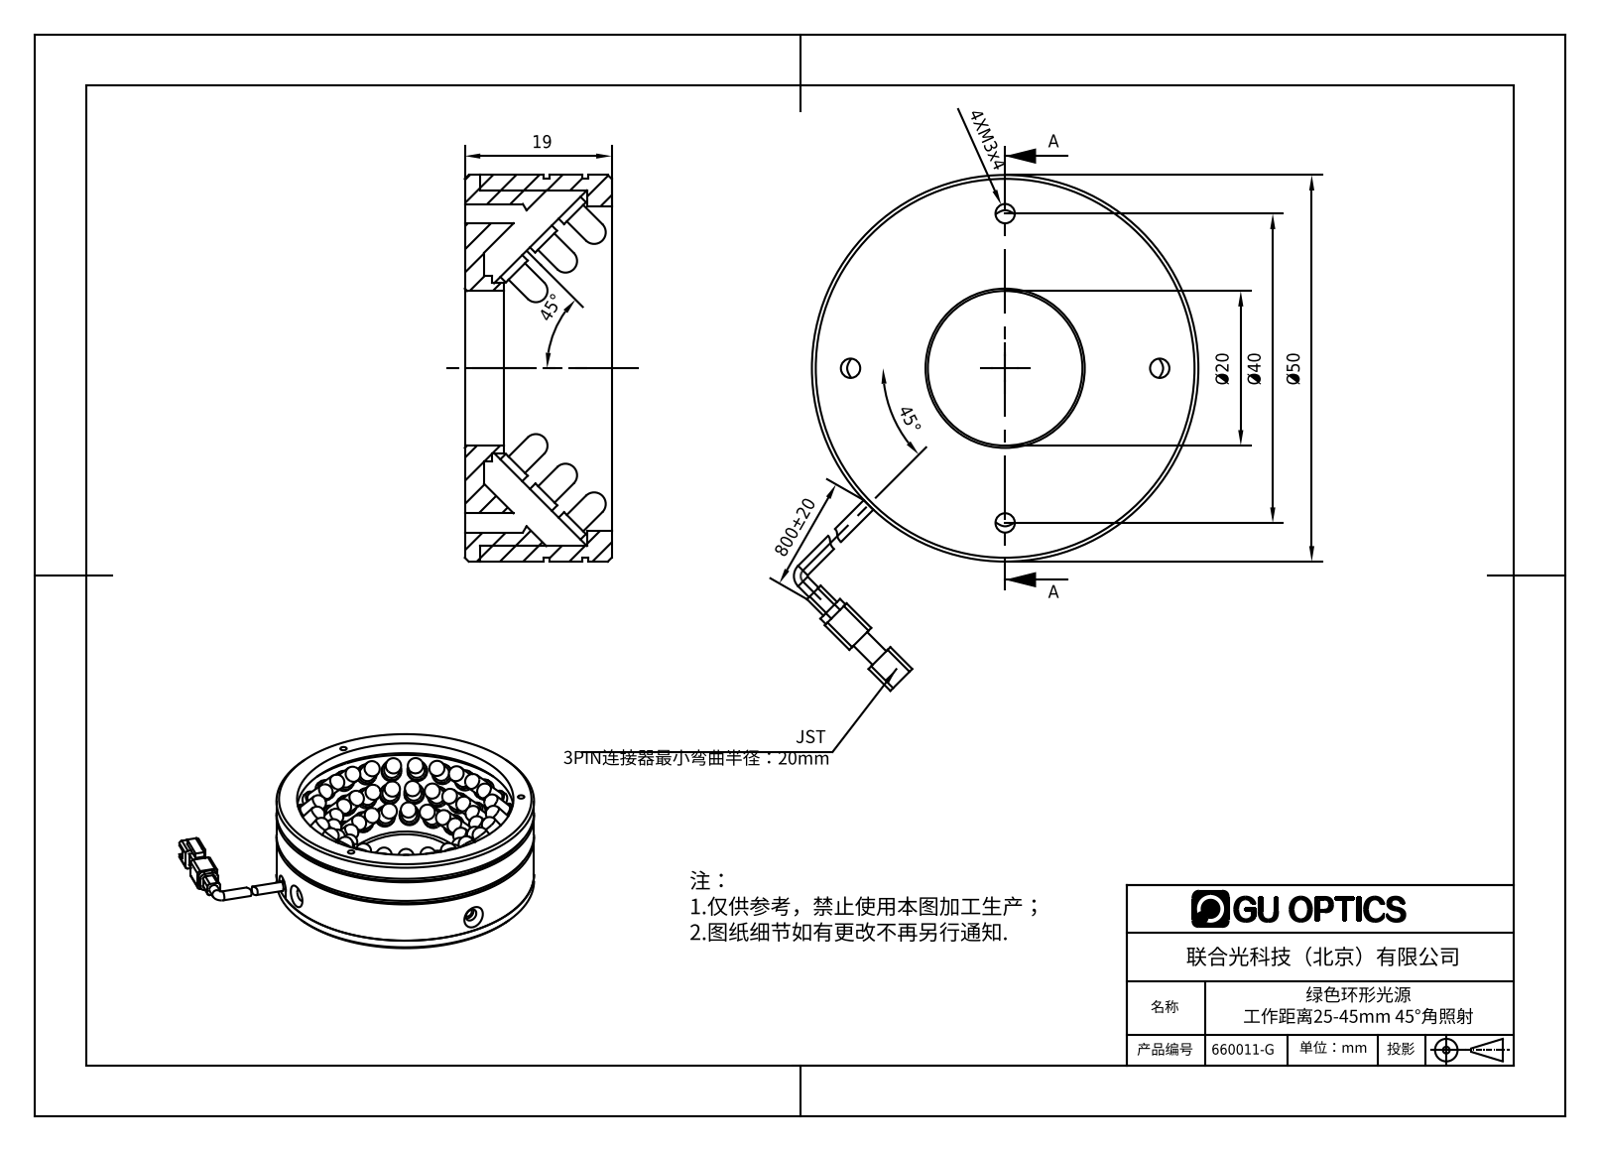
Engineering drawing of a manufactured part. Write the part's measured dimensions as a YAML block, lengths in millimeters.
part_name: "660011-G"
step_written_by: "SolidWorks 2016 (AUTOMOTIVE_DESIGN)"
units: millimeters
bodies: {solids: 70, faces: 1331, planar: 857, cylindrical: 361, other: 113}
overall_size: [66.72, 52.33, 19]
volume: 17436
surface_area: 21875
round_holes:
  - {diameter: 2.5, count: 4}
  - {diameter: 1.25, count: 3}
  - {diameter: 3, count: 3}
  - {diameter: 1.6, count: 2}
  - {diameter: 2.4, count: 2}
  - {diameter: 20, count: 1}
  - {diameter: 42, count: 1}
round_bosses_or_shafts:
  - {diameter: 3.8, count: 65}
  - {diameter: 3, count: 63}
  - {diameter: 1.75, count: 2}
  - {diameter: 50, count: 1}
  - {diameter: 49, count: 1}
  - {diameter: 46, count: 1}
  - {diameter: 24, count: 1}
  - {diameter: 22, count: 1}
partial_cylinders:
  - {radius: 0.5, count: 10}
  - {radius: 1, count: 4}
  - {radius: 1.6, count: 1}
  - {radius: 4.5, count: 1}
face_to_face_distances: [2, 0.5, 19, 17, 2.5, 1, 3, 16.5, 5, 0.8]
hole_center_spacings: [20, 28.28, 22.5, 38.97, 11.26, 30.1, 40, 2.5]
